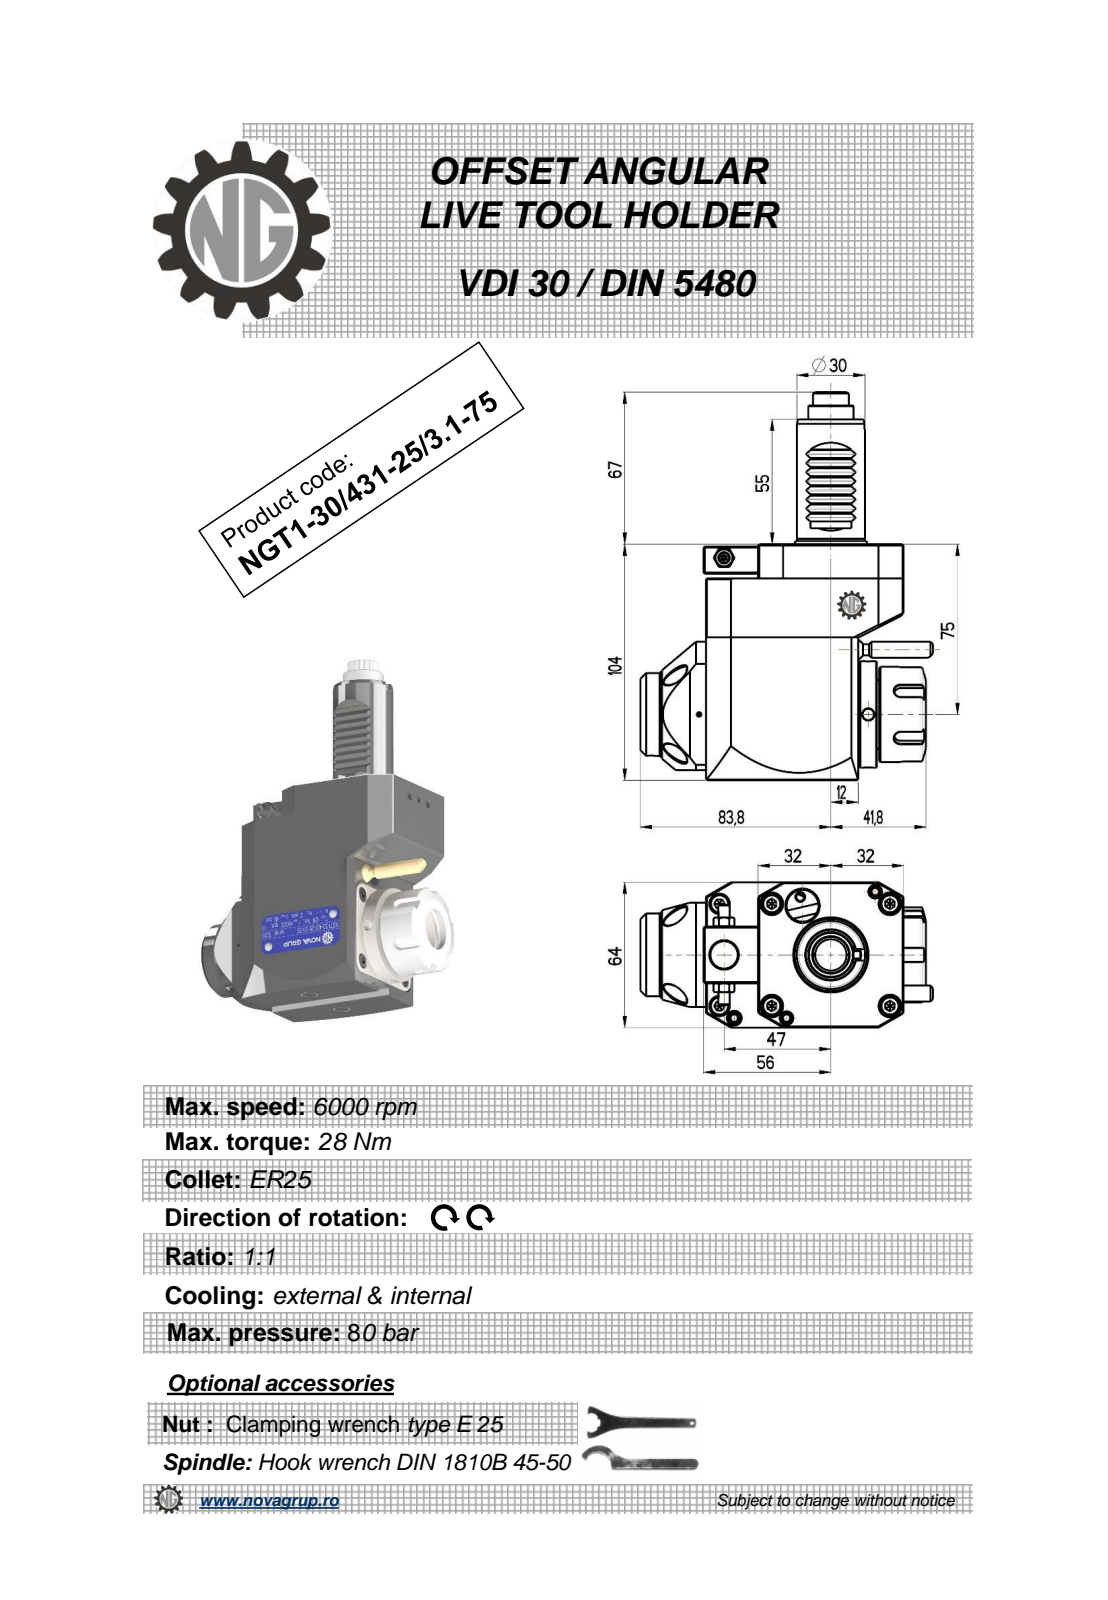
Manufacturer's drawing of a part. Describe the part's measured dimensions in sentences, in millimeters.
The part is named "NGT1_30_431_25_3_1_75". Its 3-D file was written by "PRO/ENGINEER BY PARAMETRIC TECHNOLOGY CORPORATION, 2010280 (CONFIG_CONTROL_DESIGN)". It is 1 solid with 517 faces: 196 planar, 155 cylindrical and 166 other. Overall it measures 171 by 128.63 by 64 millimeters. Its volume is 590 818 cubic millimeters and its surface area 57 169 square millimeters. Round holes: 2 of diameter 5, 1 of diameter 2.5, 1 of diameter 3, 1 of diameter 4.2, 1 of diameter 9.5, 1 of diameter 12, 1 of diameter 20.3. Round bosses or shafts: 2 of diameter 8.96, 2 of diameter 5, 1 of diameter 47, 1 of diameter 42, 1 of diameter 36.5, 1 of diameter 35, 1 of diameter 30, 1 of diameter 20. Partial cylindrical surfaces (rounded edges, fillets, slot ends): 36 of radius 1.98, 12 of radius 0.26, 8 of radius 0.3, 5 of radius 3, 2 of radius 160, 1 of radius 7.08, 1 of radius 7.92, 1 of radius 13. The main face-to-face distances are 64, 104, 87, 15, 89, 20, 19.8, 0.5, 67.2, 67. The hole center spacings are 33.19, 43, 63.45, 68, 93.74.
